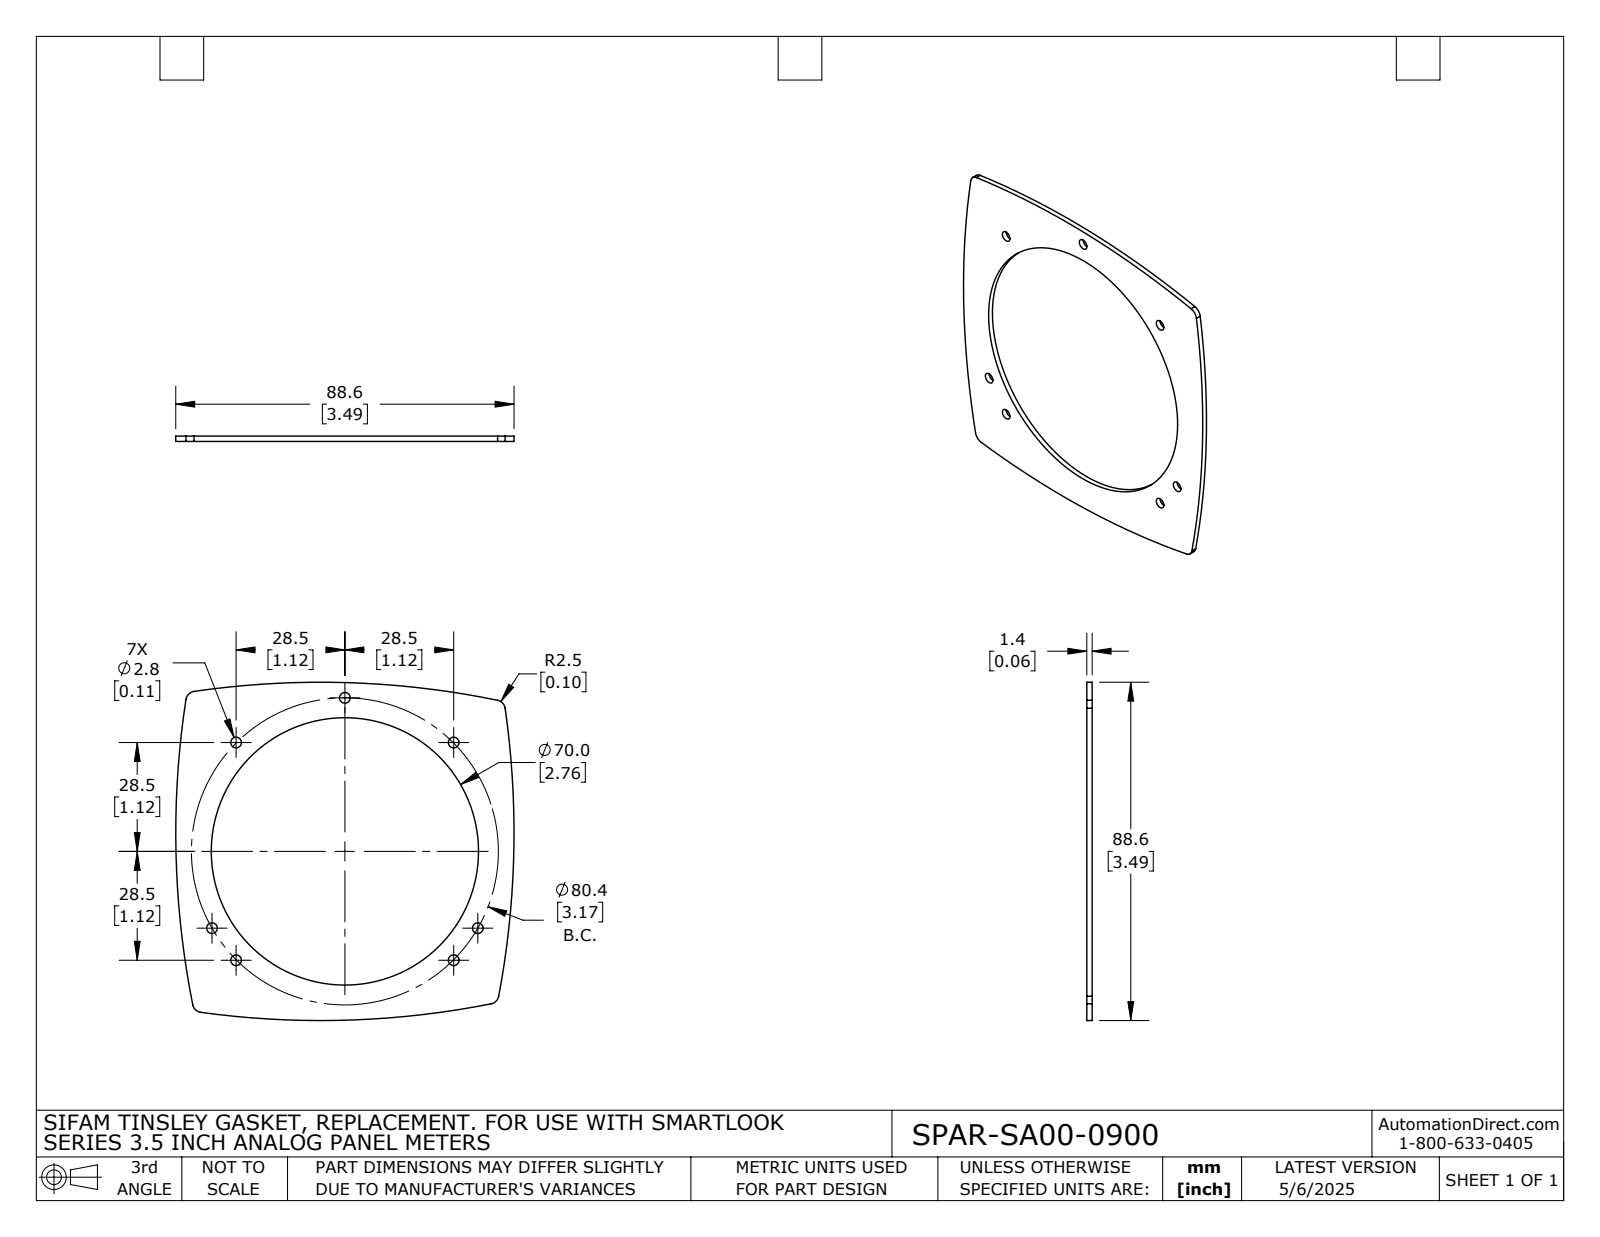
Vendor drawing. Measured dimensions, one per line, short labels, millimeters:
name: SPAR-SA00-0900
written by: SolidWorks 2021 (AUTOMOTIVE_DESIGN)
unit: mm
bodies: 1 solid, 27 faces (2 planar, 25 cylindrical, 0 other)
size: 88.6 × 88.5 × 1.4
volume: 4 870 mm³; area: 7 806 mm²
holes: 7× ⌀2.8, 1× ⌀70
rounds: 4× R2.5, 4× R229.8
face distances: 1.4
hole spacings: 40.3, 57, 40.2, 10.5, 30.8, 49, 63.9, 69.6
